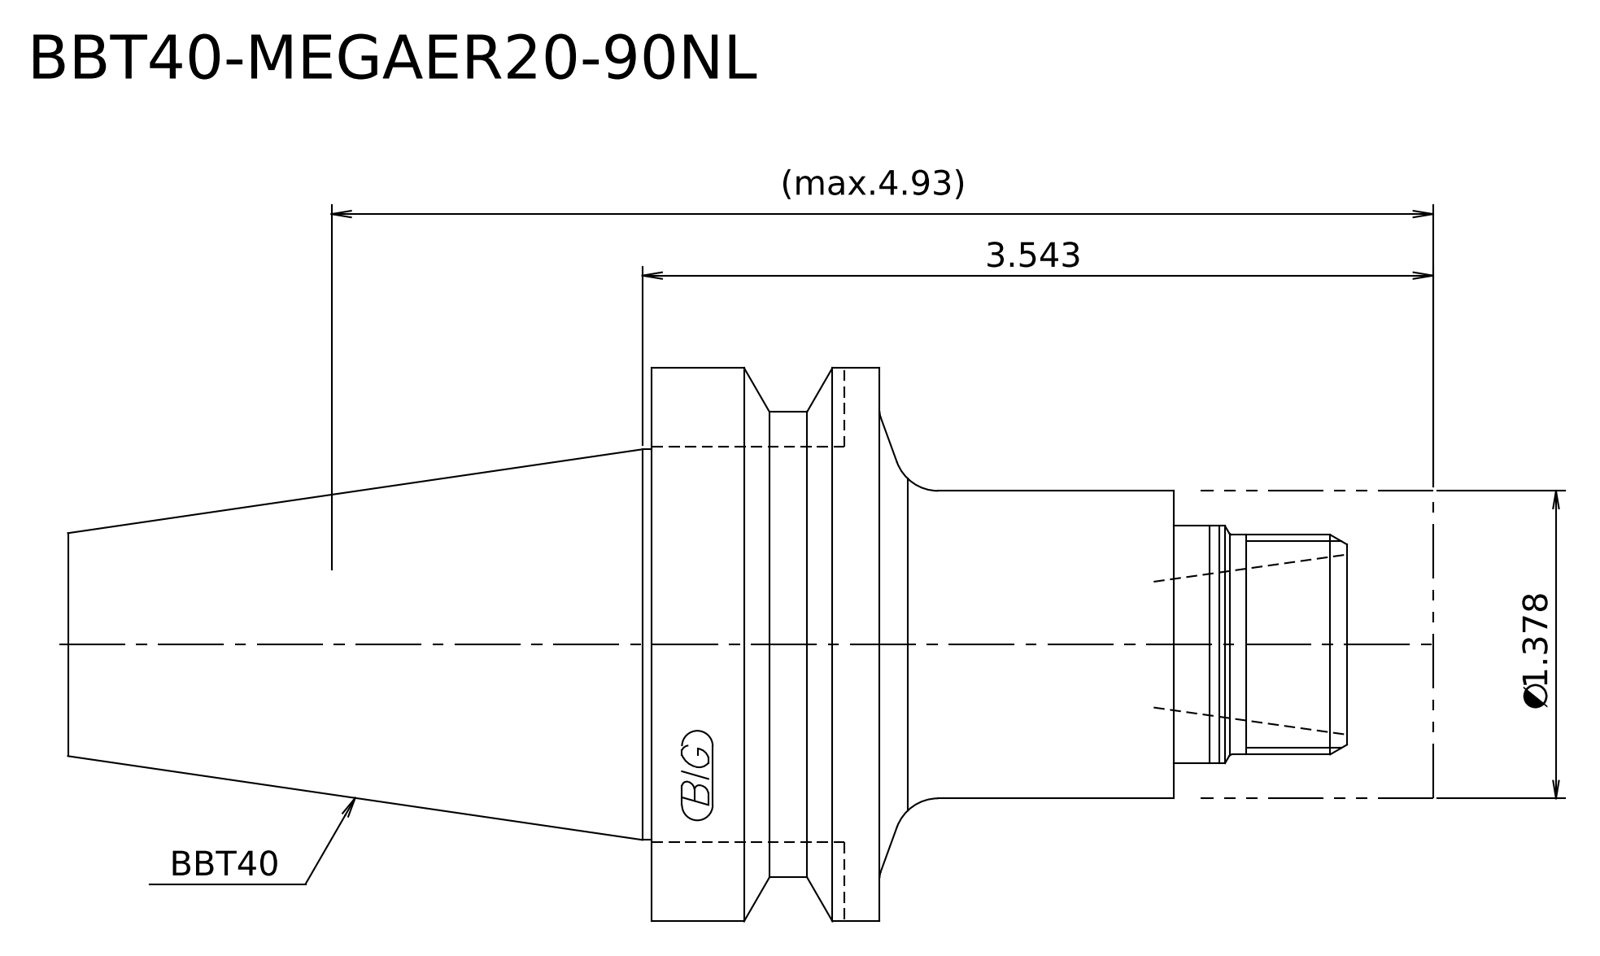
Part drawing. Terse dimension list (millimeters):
written by: Kubotek KeyCreator 2011 V10.0.2 (22737) (automotive_design)
unit: mm
bodies: 2 solids, 21 faces (7 planar, 8 cylindrical, 6 other)
size: 155.4 × 63 × 63
volume: 211 847 mm³; area: 28 125 mm²
bosses: 1× ⌀63, 1× ⌀53, 1× ⌀44.45, 1× ⌀35, 1× ⌀27, 1× ⌀25
face distances: 62.5, 26.5, 89, 63, 36.5, 26, 155.4, 128.9, 92.4, 66.4
